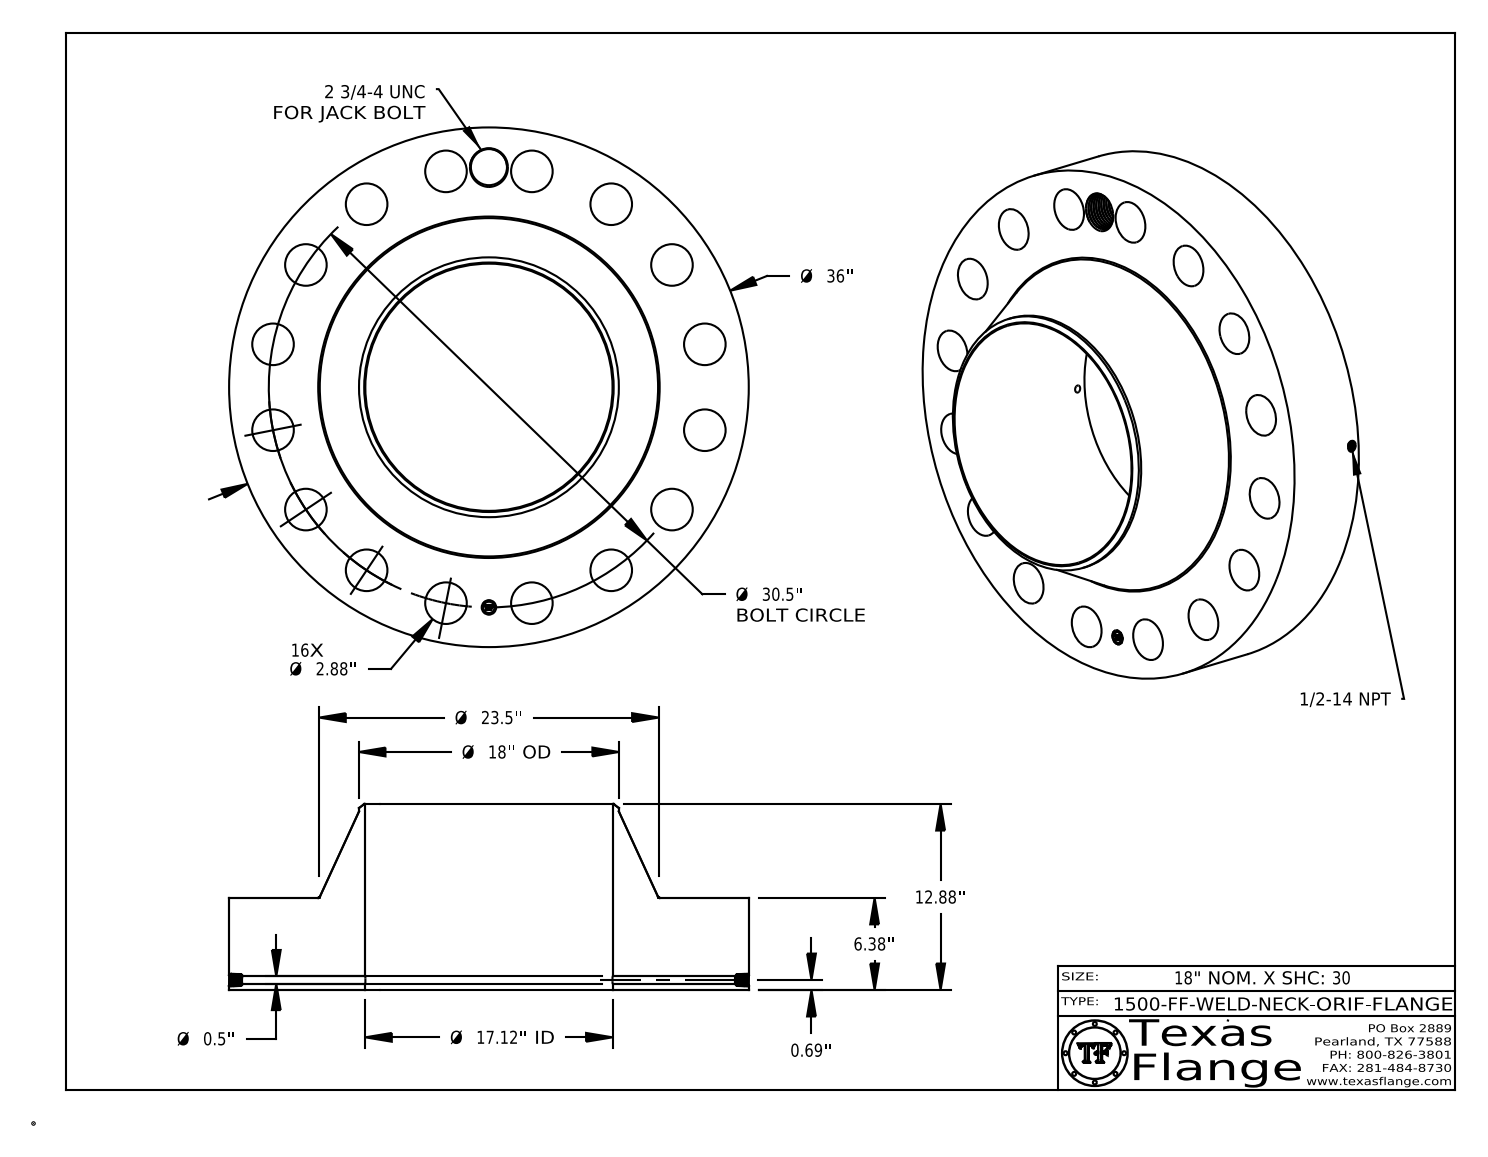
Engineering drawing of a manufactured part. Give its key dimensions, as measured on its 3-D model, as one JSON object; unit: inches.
{"part_name": "1500-FF-WELD-NECK", "step_written_by": "CATIA V5 STEP AP214 (AUTOMOTIVE_DESIGN)", "units": "inches", "bodies": {"solids": 1, "faces": 846, "planar": 368, "cylindrical": 129, "other": 349}, "overall_size": [36, 36, 12.88], "volume_in3": 4988, "surface_area_in2": 4069, "round_holes": [[2.88, 16], [0.5, 1], [0.672, 1], [1, 1], [2.5, 1], [17.124, 1]], "round_bosses_or_shafts": [[0.061, 8], [36, 1], [18, 1], [0.788, 1]], "face_to_face_distances": [6.38, 12.88, 6.5, 6.365, 0.015, 6.515, 0.298, 0.293, 0.054, 0.248], "hole_center_spacings": [15.25, 5.95, 11.672, 16.945, 21.567, 28.178, 25.36, 29.914]}
